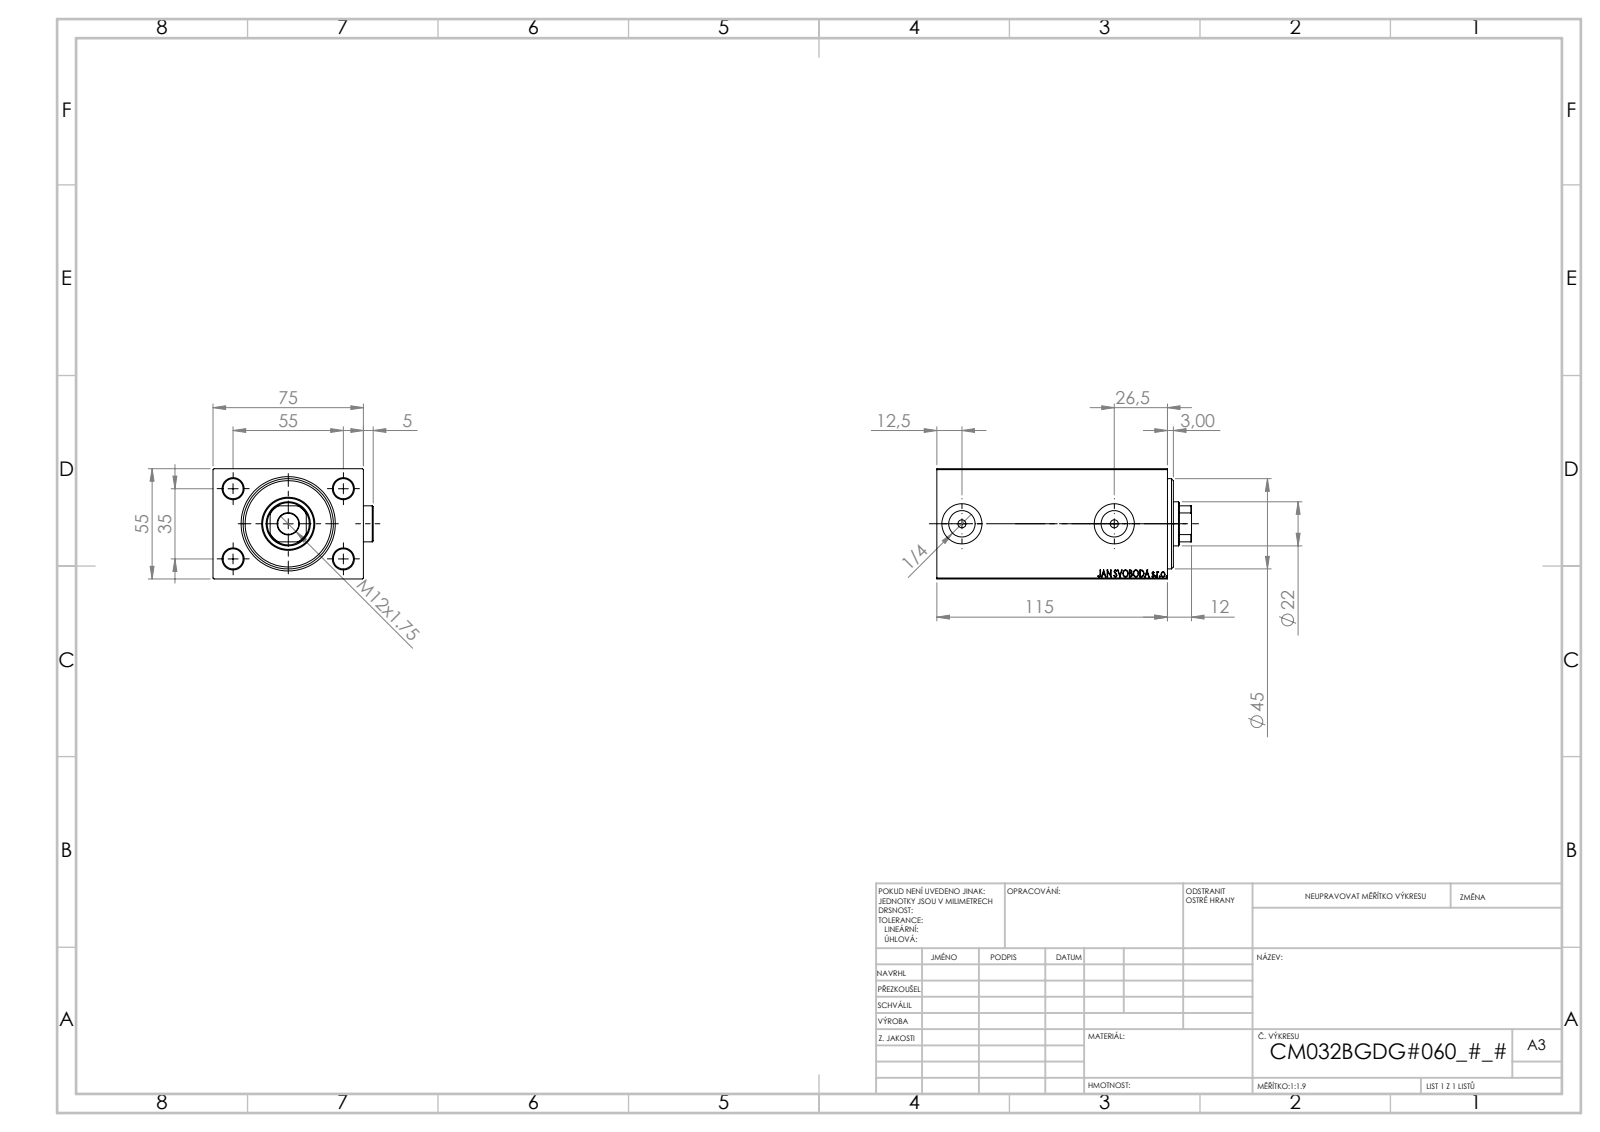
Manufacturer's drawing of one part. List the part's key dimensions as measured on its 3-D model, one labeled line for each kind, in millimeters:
Part name (STEP PRODUCT): V450CM_B_VCP; V450CM_VC_B; Zatka_OIL_PORT; V450CM_B_Body
STEP written by: SolidWorks 2019 (CONFIG_CONTROL_DESIGN)
Units: millimetres
Bodies: 5 solids, 935 faces (435 planar, 70 cylindrical, 430 other)
Overall size (bounding box): 127 × 79.9 × 55
Volume: 436 116 mm³ · Surface area: 74 629 mm²
Round holes (diameter × count): ⌀10 ×4, ⌀4 ×2, ⌀13.16 ×2, ⌀20 ×2, ⌀10.5 ×1, ⌀22 ×1, ⌀25.5 ×1, ⌀26.5 ×1, ⌀32 ×1, ⌀34 ×1, ⌀45 ×1
Round bosses / shafts (diameter × count): ⌀18 ×2
Partial cylindrical surfaces — rounded edges, fillets, slot ends (radius × count): R10.5 ×1
Main face-to-face distances: 55, 75, 115, 5, 105, 10, 100, 110, 74.9, 3
Hole centre spacings: 32.6, 35, 55, 65.19, 76
